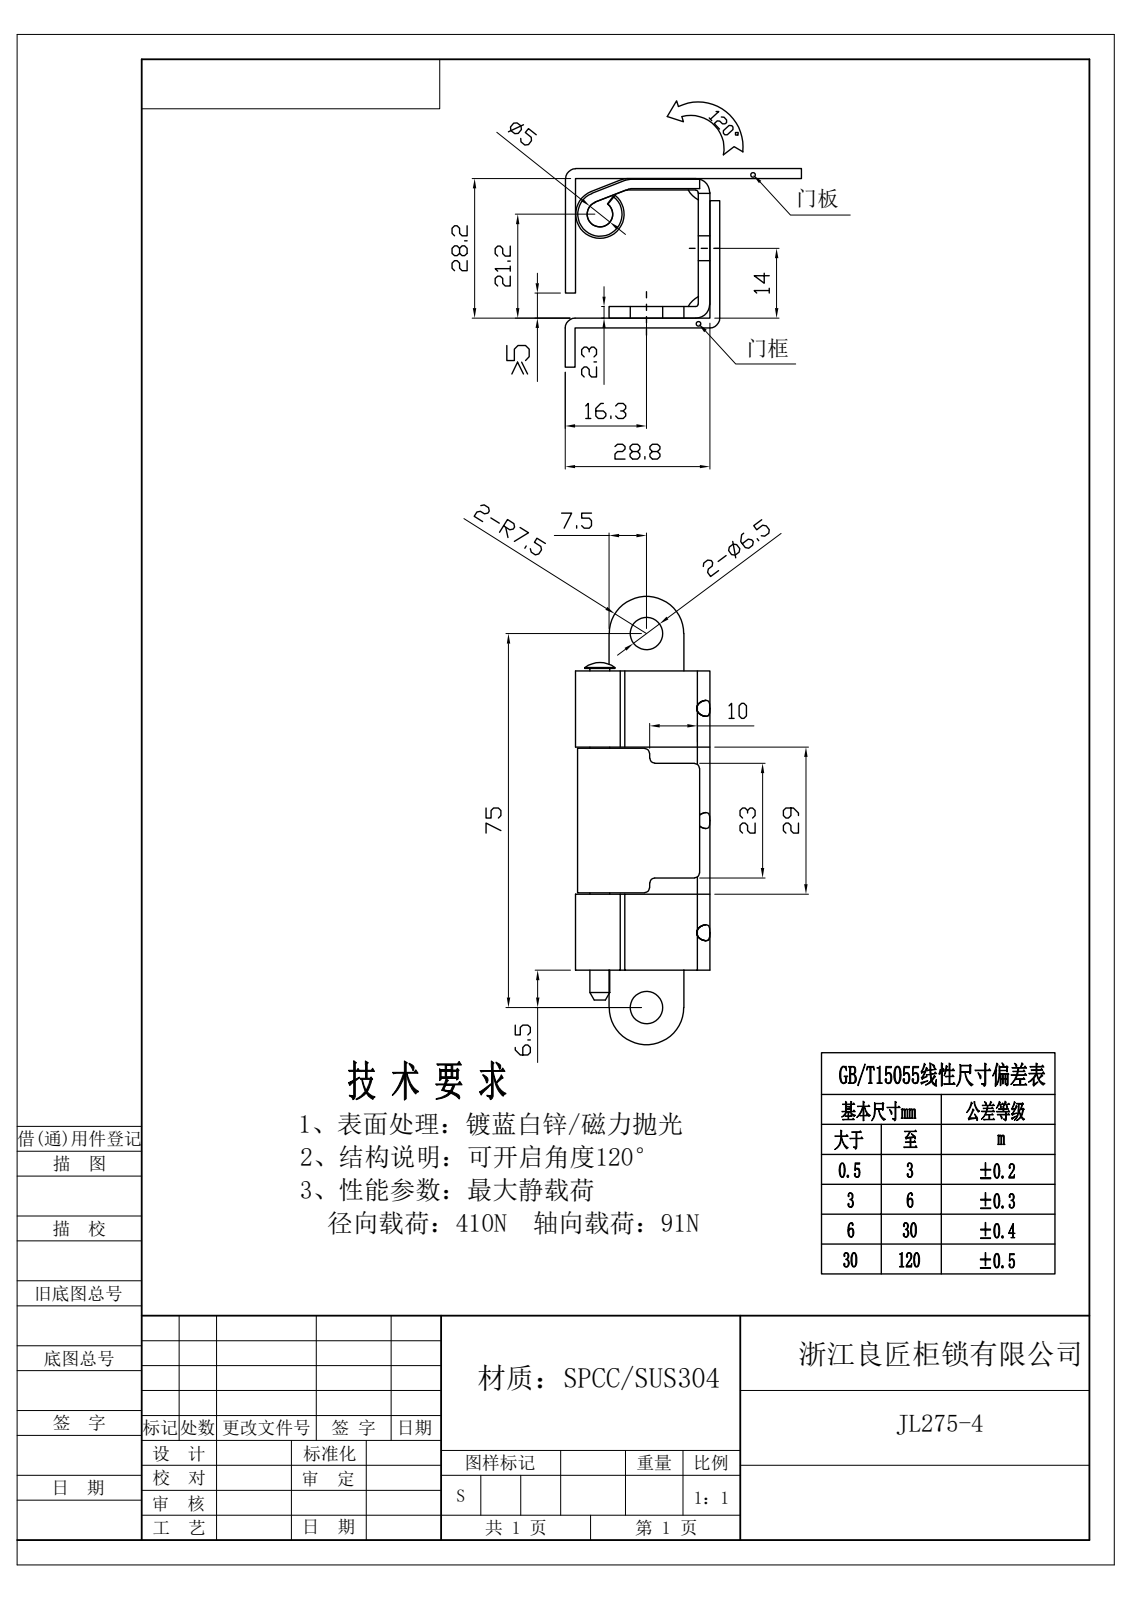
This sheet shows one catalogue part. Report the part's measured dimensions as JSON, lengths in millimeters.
{"step_written_by": "Rhino 8.5 (CONFIG_CONTROL_DESIGN)", "units": "millimeters", "bodies": {"solids": 2, "faces": 78, "planar": 40, "cylindrical": 34, "other": 4}, "overall_size": [75, 28, 26.92], "volume_mm3": 2957, "surface_area_mm2": 12195, "round_holes": [[6.5, 2], [5, 1], [5.15, 1]], "round_bosses_or_shafts": [[9.75, 1], [8.95, 1], [6, 1], [4, 1]], "partial_cylinders_radius": [[1, 8], [0.5, 2], [2.8, 2], [2.9, 1], [3.3, 1]], "face_to_face_distances": [2.3, 25.7, 1.9, 23.4, 28, 2.05, 27.85, 25.55, 2.15, 25.95], "hole_center_spacings": [60]}
